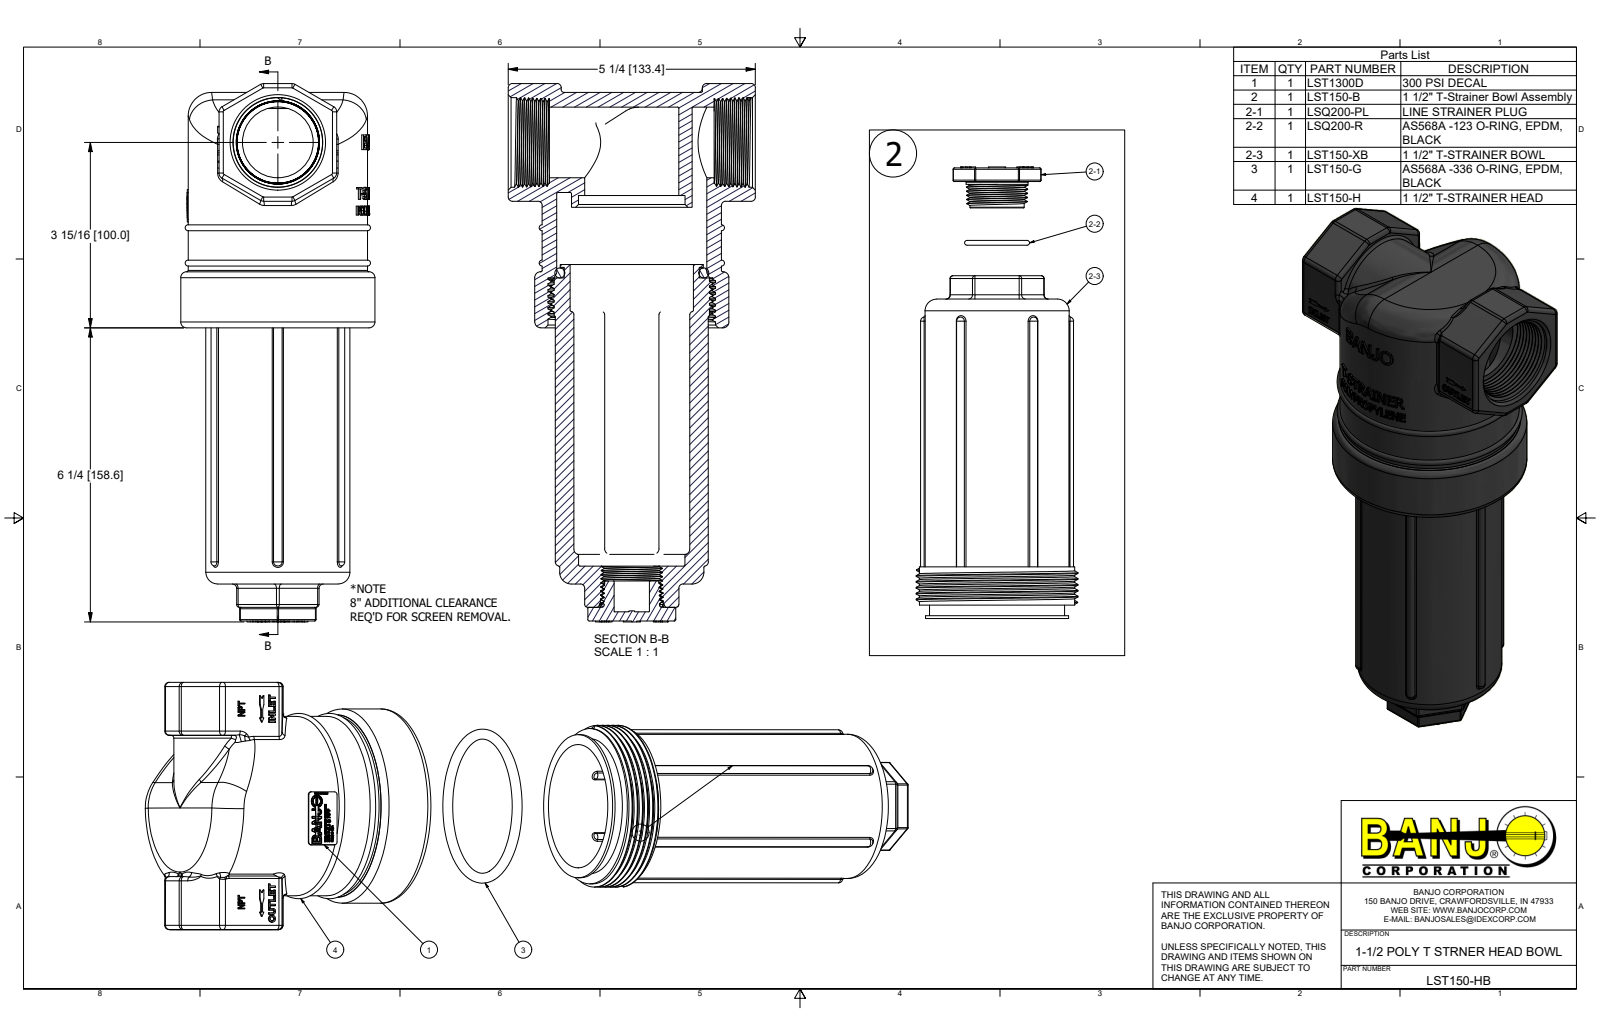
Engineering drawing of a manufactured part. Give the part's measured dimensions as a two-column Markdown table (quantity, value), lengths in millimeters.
| quantity | value |
| --- | --- |
| part name | LST150-HB; CE050D; LST1300D; LST150-B (+5 more) |
| STEP written by | Autodesk Inventor 2018 (AUTOMOTIVE_DESIGN) |
| units | millimeters |
| bodies | 7 solids, 2808 faces (1512 planar, 261 cylindrical, 1035 other) |
| overall size | 290.4 × 133.4 × 104.8 |
| volume | 766 400 mm³ |
| surface area | 236 800 mm² |
| round holes (diameter × count) | 4.6 × 1, 6.5 × 1, 19.1 × 1, 38.1 × 1, 50.8 × 1, 57.4 × 1, 57.5 × 1, 66.5 × 1, 81 × 1, 87 × 1, 90.4 × 1 |
| round bosses / shafts (diameter × count) | 104.8 × 1, 96.8 × 1, 87.2 × 1, 83.8 × 1, 77.8 × 1, 77.2 × 1, 72.9 × 1, 65.1 × 1 |
| partial cylindrical surfaces (radius × count) | 0.8 × 44, 2.3 × 34, 1.5 × 16, 3.2 × 10, 2 × 6, 2.4 × 6, 0.7 × 2, 0.8 × 2 |
| main face-to-face distances | 63.5, 100.1, 22.2, 155.4, 255.5, 247.6, 92.2, 8, 9.7, 165.1 |
